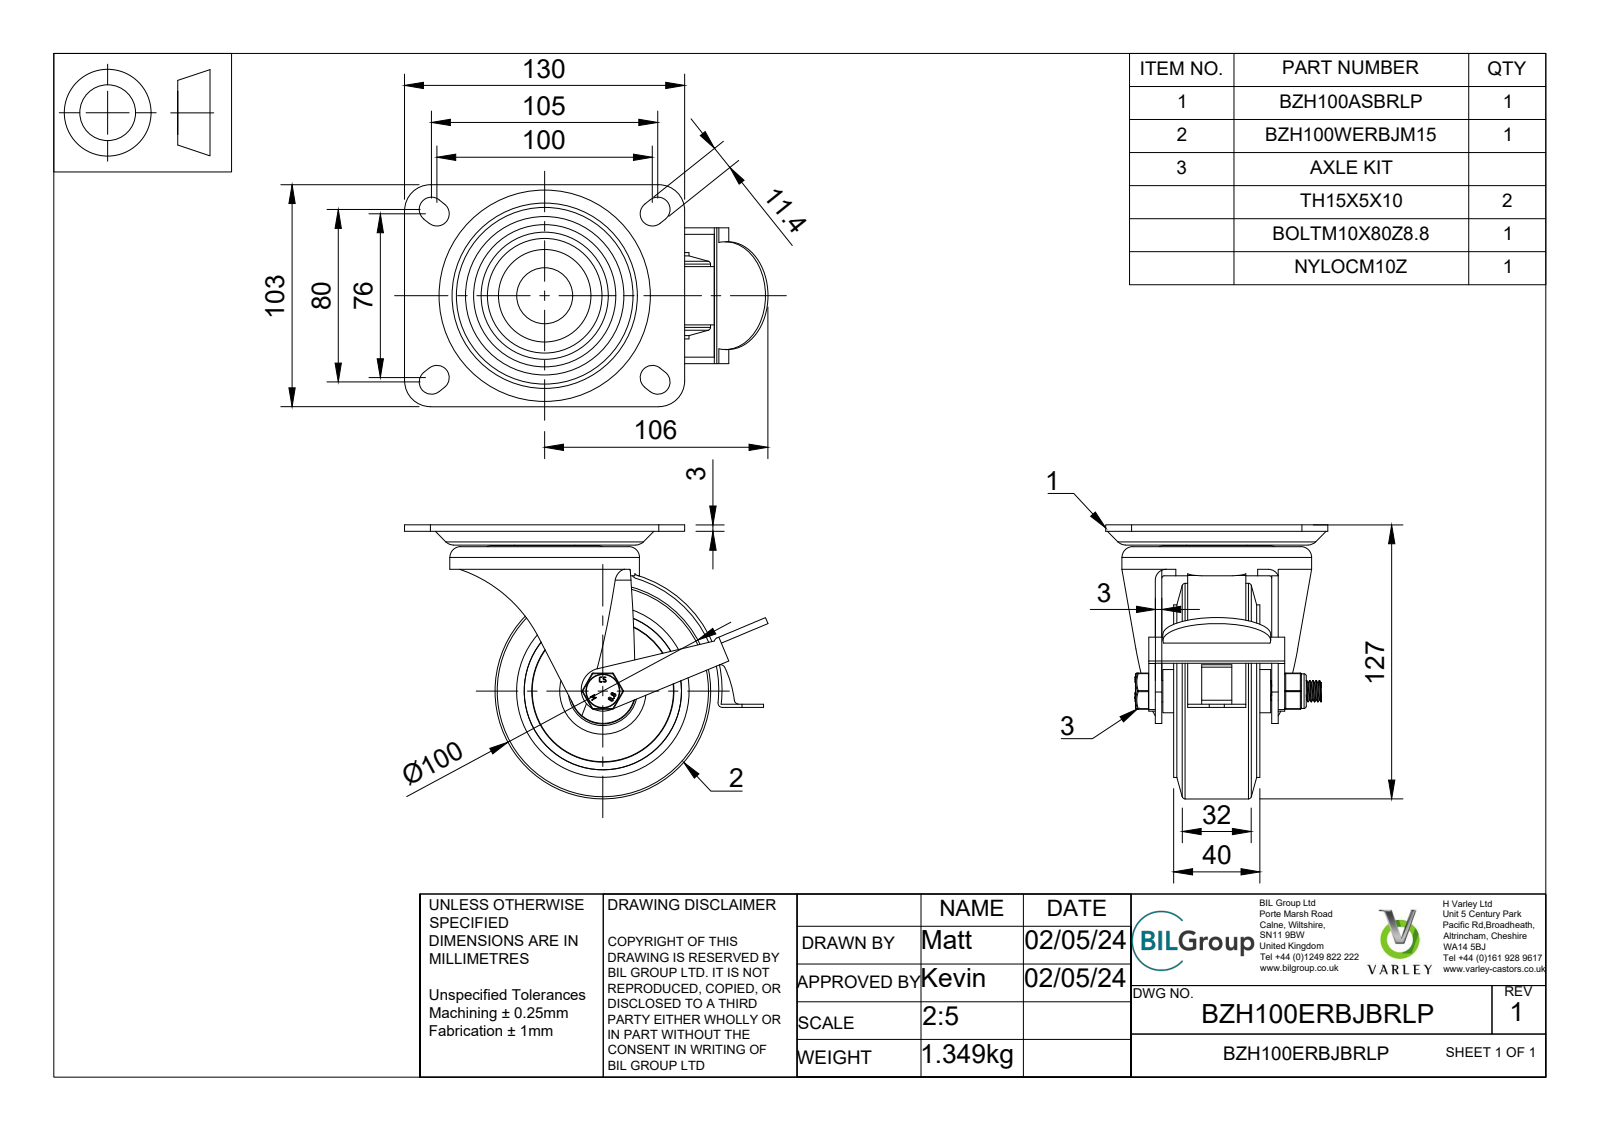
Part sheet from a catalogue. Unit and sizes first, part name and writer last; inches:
Units: inches
Overall size (bounding box): 6.64 × 5.005 × 4.055
Round holes (diameter × count): ⌀0.394 ×1, ⌀0.413 ×1, ⌀0.472 ×1, ⌀0.591 ×1, ⌀0.709 ×1, ⌀0.787 ×1, ⌀0.827 ×1, ⌀1.079 ×1, ⌀1.181 ×1, ⌀1.26 ×1, ⌀2.874 ×1, ⌀3.228 ×1
Round bosses / shafts (diameter × count): ⌀1.102 ×2, ⌀3.937 ×1, ⌀3.465 ×1, ⌀3.15 ×1, ⌀1.575 ×1, ⌀1.417 ×1, ⌀1.118 ×1, ⌀1.024 ×1
Partial cylindrical surfaces — rounded edges, fillets, slot ends (radius × count): R0.02 ×18, R0.079 ×8, R0.224 ×8, R0.013 ×4, R0.025 ×4, R0.472 ×4, R0.394 ×3, R0.025 ×2
Main face-to-face distances: 0.118, 0.335, 0.63, 0.945, 2.244, 0.965, 1.28, 1.909, 0.315, 1.575
Volume: 20.83 in³ · Surface area: 246.4 in²
Bodies: 40 solids, 1121 faces (464 planar, 225 cylindrical, 432 other)
Part name (STEP PRODUCT): BZH100ERBJBRLP v3; BZH100ASBRLP v1; ZINC PLATED, PRESSED STEEL TOP PLATE; ZINC PLATED, PRESSED STEEL FORKS (+8 more)
STEP written by: Autodesk Translation Framework v12.20.1.177 (AUTOMOTIVE_DESIGN)
